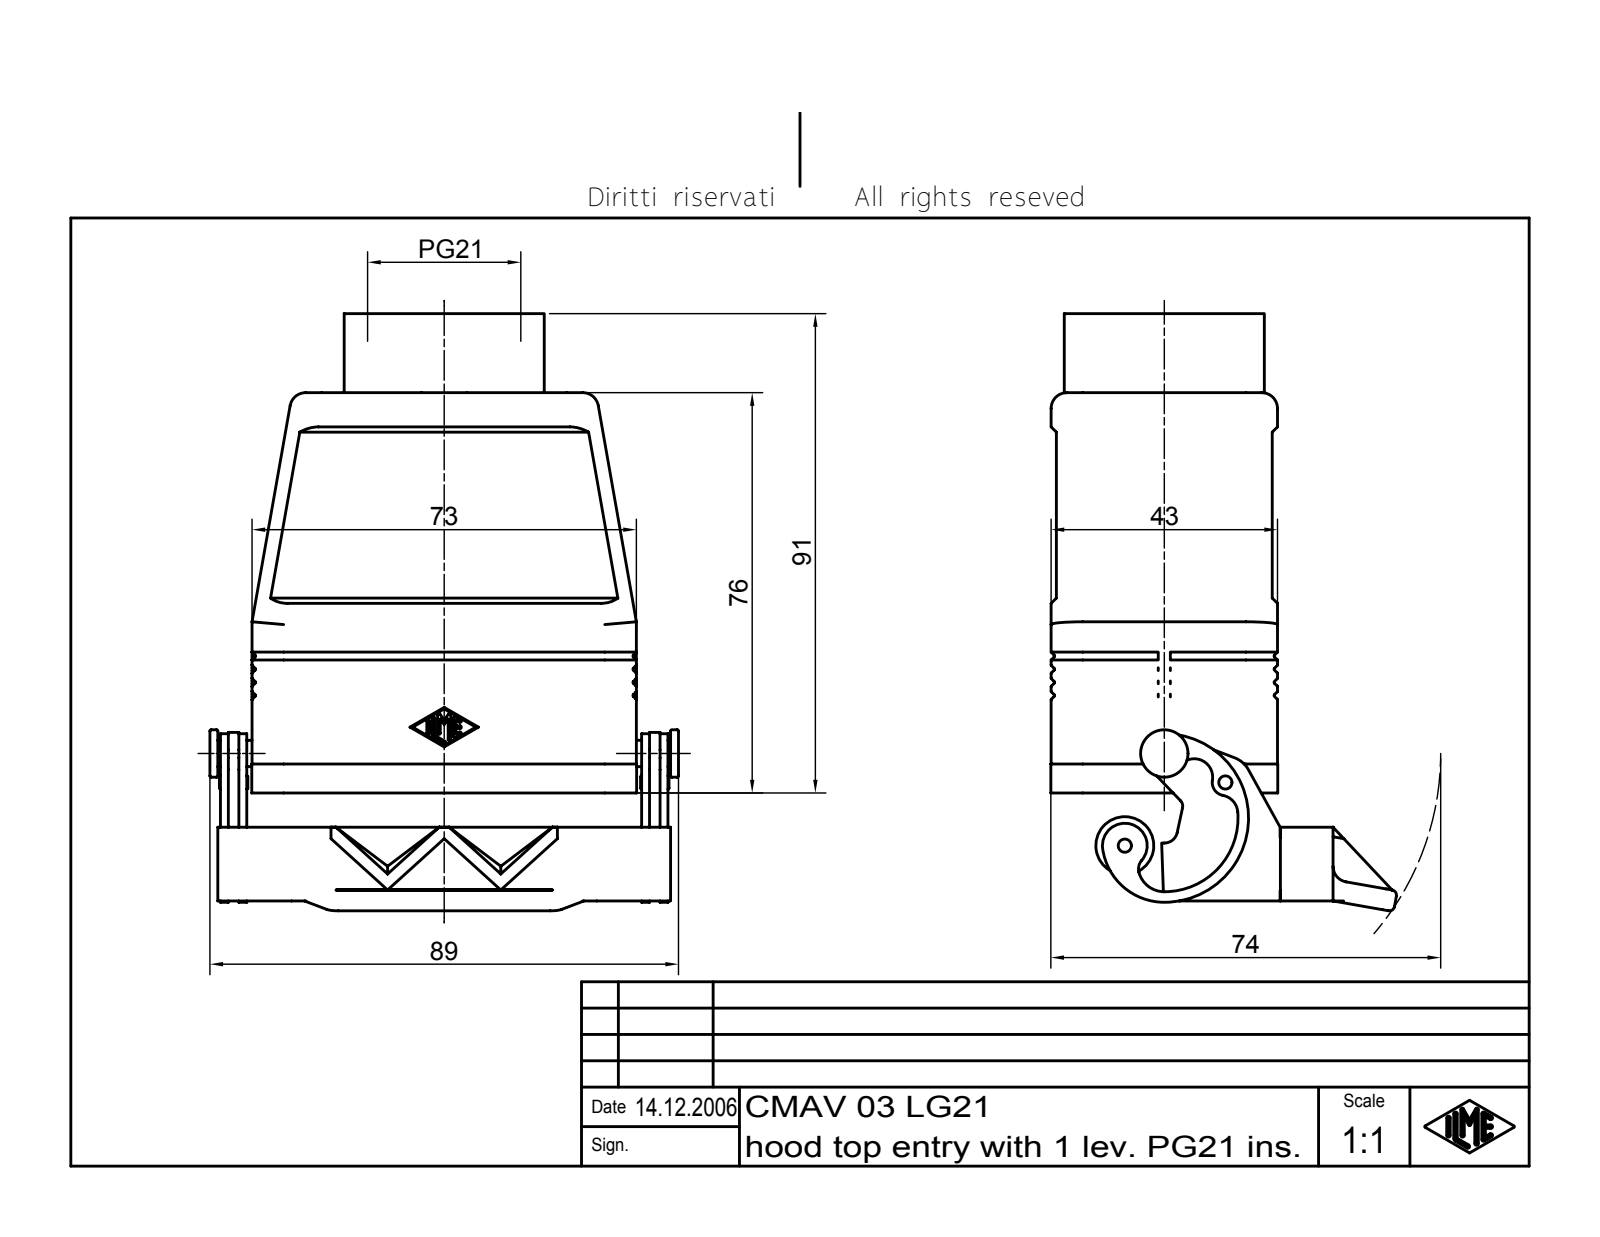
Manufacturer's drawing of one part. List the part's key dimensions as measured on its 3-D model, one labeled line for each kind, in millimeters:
Part name (STEP PRODUCT): CMAV 03 LG21
STEP written by: Autodesk Inventor 7 (AUTOMOTIVE_DESIGN)
Units: millimetres
Bodies: 1 solid, 847 faces (192 planar, 300 cylindrical, 355 other)
Overall size (bounding box): 113.37 × 89 × 65.64
Volume: 86 386 mm³ · Surface area: 48 687 mm²
Round holes (diameter × count): ⌀2.5 ×1, ⌀24.78 ×1, ⌀26.78 ×1
Round bosses / shafts (diameter × count): ⌀38 ×1, ⌀11 ×1, ⌀9 ×1, ⌀5 ×1, ⌀3.1 ×1, ⌀2 ×1
Partial cylindrical surfaces — rounded edges, fillets, slot ends (radius × count): R0.2 ×52, R0.25 ×26, R2.5 ×11, R6 ×8, R3 ×7, R1 ×6, R2.45 ×4, R6.05 ×4
Main face-to-face distances: 3.45, 3.5, 39.55, 39.5, 36.05, 36, 2.45, 3.55, 36.1, 2.5
